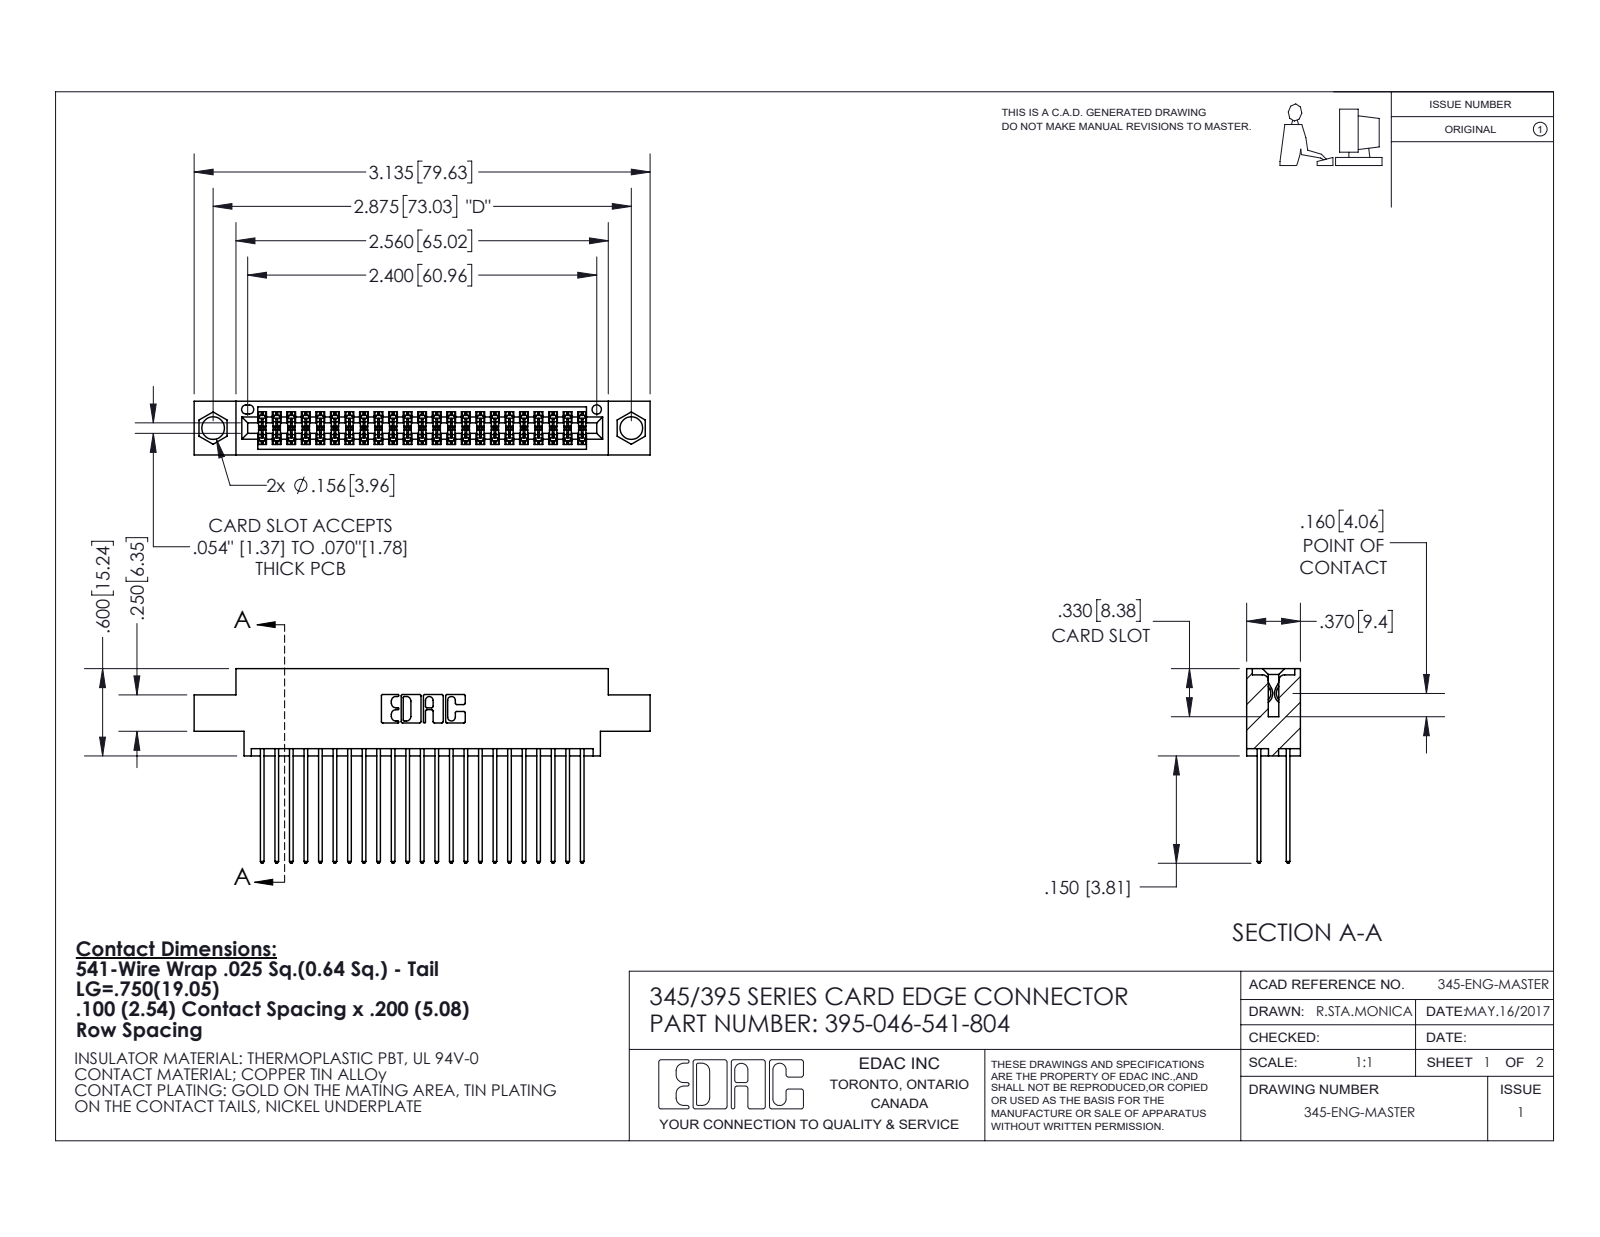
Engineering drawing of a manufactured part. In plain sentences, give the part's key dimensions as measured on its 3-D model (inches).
The part is named "345 Part_0.170 Offset - 0.156 Dia-TI; 395-046-541-804; 345-292-001_345-293-141". Its 3-D file was written by "SolidWorks 2020 (CONFIG_CONTROL_DESIGN)". It is 47 solids with 2444 faces: 1616 planar, 828 cylindrical and 0 other. Overall it measures 3.135 by 1.337 by 0.37 inches. Its volume is 0.464 cubic inches and its surface area 18.77 square inches. Round holes: 2 of diameter 0.156, 1 of diameter 0.064. Partial cylindrical surfaces (rounded edges, fillets, slot ends): 92 of radius 0.006, 46 of radius 0.01, 22 of radius 0.01, 6 of radius 0.007, 6 of radius 0.031, 3 of radius 0.026, 2 of radius 0.014, 2 of radius 0.019. The main face-to-face distances are 0.072, 0.298, 0.2, 0.098, 0.272, 0.025, 0.37, 0.225, 0.175, 0.149. The hole center spacings are 0.27, 2.641, 2.875.
